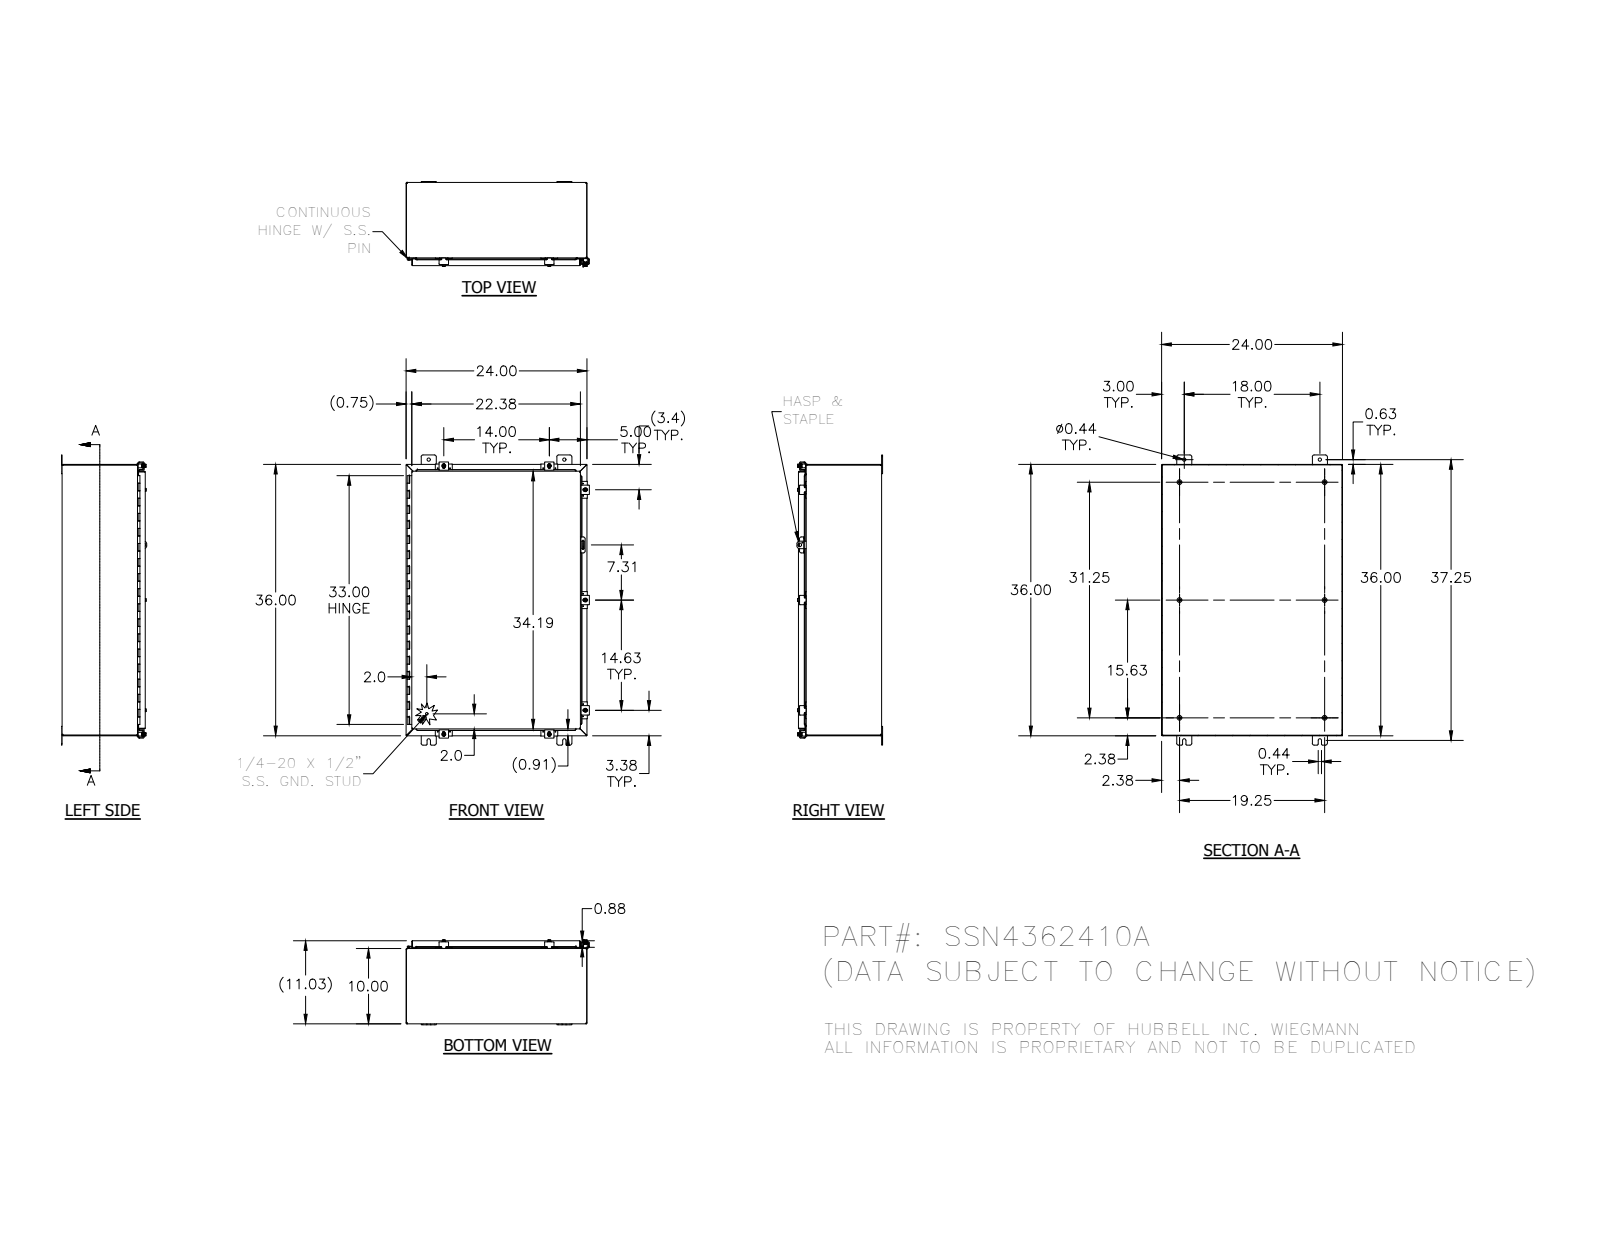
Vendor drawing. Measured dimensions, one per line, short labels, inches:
name: 38846; SSN4362410A; 38859; 34871 (+8 more)
written by: SolidWorks 2014 (AUTOMOTIVE_DESIGN)
unit: in
bodies: 54 solids, 2180 faces (862 planar, 947 cylindrical, 371 other)
size: 38.5 × 24.216 × 11.355
volume: 258.3 in³; area: 6 813 in²
holes: 14× ⌀0.11, 7× ⌀0.211, 7× ⌀0.281, 7× ⌀0.3, 4× ⌀0.438, 1× ⌀0.125, 1× ⌀0.156, 1× ⌀0.5
bosses: 9× ⌀0.25, 7× ⌀0.52, 7× ⌀0.5, 7× ⌀0.35, 6× ⌀0.625, 6× ⌀0.33, 1× ⌀0.337, 1× ⌀0.12
rounds: 83× R0.03, 37× R0.125, 33× R0.25, 23× R0.031, 23× R0.105, 18× R0.062, 14× R0.141, 10× R0.1
face distances: 0.074, 10.959, 10.885, 11.033, 23.926, 35.926, 24, 23.852, 9.926, 1.033
hole spacings: 0.876, 35.298, 14, 1.625, 13.191, 14.816, 34.961, 34.998
